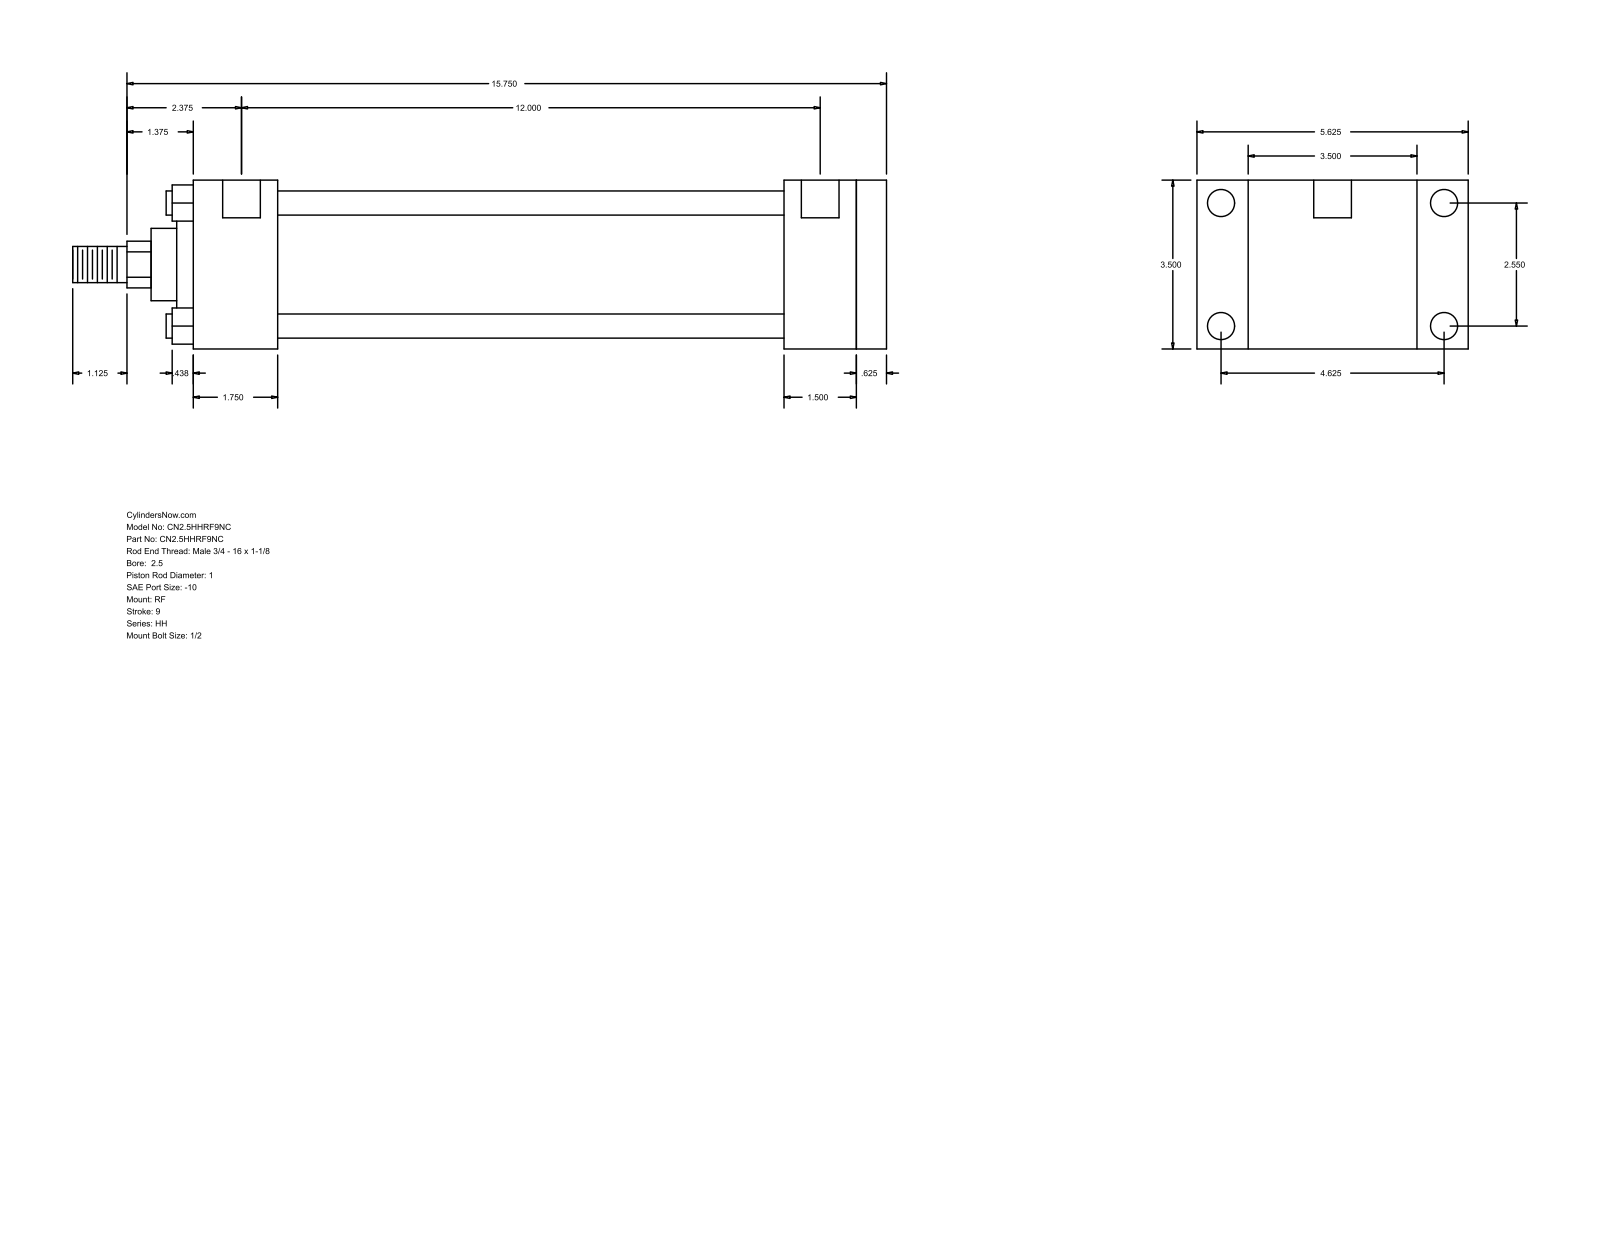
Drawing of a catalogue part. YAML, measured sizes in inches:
part_name: "HH_RF__0250_1"
step_written_by: "GSSL Pune (CONFIG_CONTROL_DESIGN)"
units: inches
bodies: {solids: 0, faces: 94, planar: 65, cylindrical: 29, other: 0}
overall_size: [16.875, 5.625, 3.5]
round_holes:
  - {diameter: 0.219, count: 4}
  - {diameter: 0.563, count: 4}
  - {diameter: 0.781, count: 2}
round_bosses_or_shafts:
  - {diameter: 0.5, count: 4}
  - {diameter: 2.875, count: 1}
  - {diameter: 2.375, count: 1}
  - {diameter: 1.5, count: 1}
  - {diameter: 1, count: 1}
  - {diameter: 0.75, count: 1}
partial_cylinders:
  - {radius: 0.484, count: 1}
face_to_face_distances: [3.5, 0.625, 13.75, 14.375, 1.75, 12, 12.625, 12.25, 10.5, 1.5]
hole_center_spacings: [0.063, 2.55, 4.625, 5.281, 12.062, 12.125, 12]
